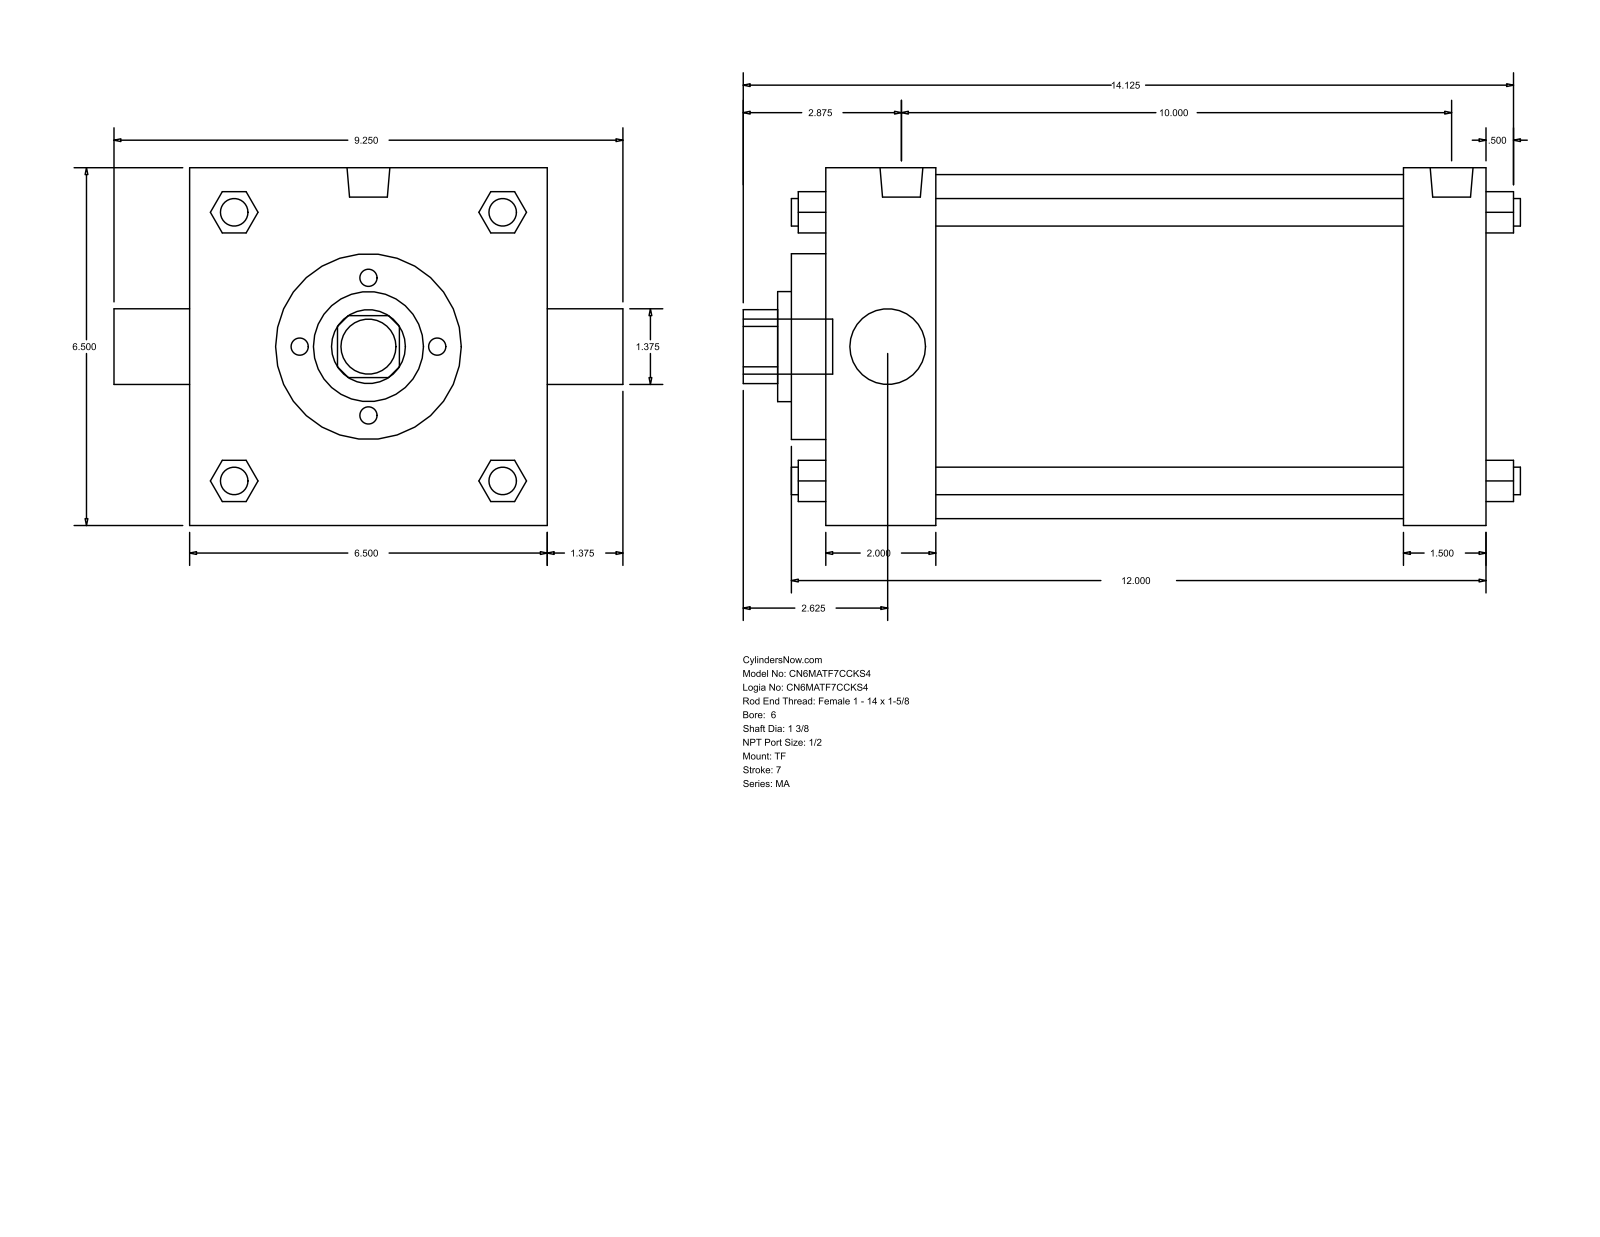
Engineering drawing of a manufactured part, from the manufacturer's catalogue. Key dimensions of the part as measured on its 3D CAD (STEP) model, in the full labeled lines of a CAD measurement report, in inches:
Part name (STEP PRODUCT): MA_TF__0600_1.375
STEP written by: GSSL Pune (CONFIG_CONTROL_DESIGN)
Units: inches
Bodies: 0 solids, 122 faces (93 planar, 29 cylindrical, 0 other)
Overall size (bounding box): 14.125 × 9.25 × 6.5
Round holes (diameter × count): ⌀1.375 ×2, ⌀2 ×1, ⌀3.375 ×1, ⌀6.25 ×1
Round bosses / shafts (diameter × count): ⌀0.5 ×4, ⌀0.687 ×3, ⌀0.778 ×2, ⌀1 ×1
Partial cylindrical surfaces — rounded edges, fillets, slot ends (radius × count): R0.672 ×1
Main face-to-face distances: 6.5, 12.125, 2, 10.125, 10.625, 8.625, 1.5, 0.625, 2.625, 11.25
